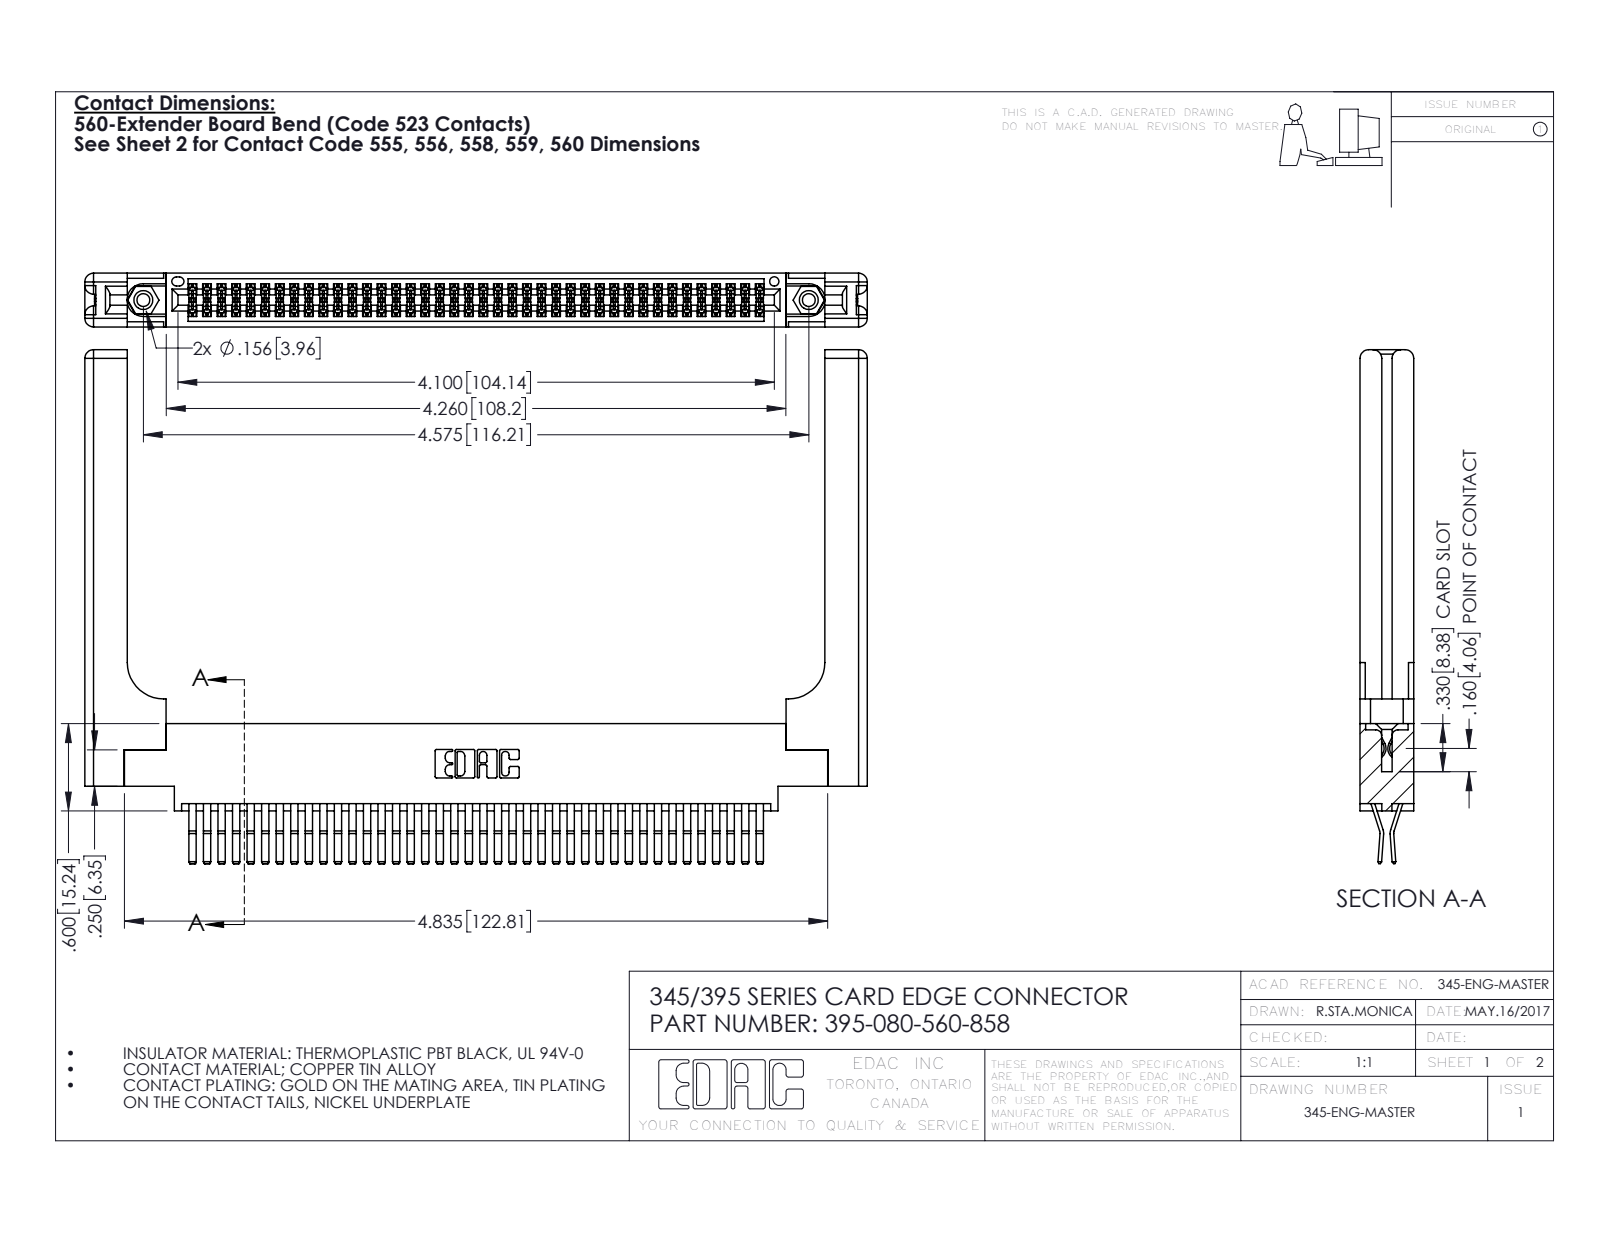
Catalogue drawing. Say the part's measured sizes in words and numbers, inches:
The part is named "345 Part_0.170 Offset - 0.156 Dia-TH; 345-250-001_345-250-001-102; 395-080-560-858; 345-292-001_560 Tail (+1 more)". Its 3-D file was written by "SolidWorks 2016 (CONFIG_CONTROL_DESIGN)". It is 85 solids with 4546 faces: 2872 planar, 1614 cylindrical and 60 other. Overall it measures 5.379 by 3.532 by 0.37 inches. Its volume is 1.351 cubic inches and its surface area 41.4 square inches. Round holes: 2 of diameter 0.089, 2 of diameter 0.125, 2 of diameter 0.156, 1 of diameter 0.064. Round bosses or shafts: 2 of diameter 0.155. Partial cylindrical surfaces (rounded edges, fillets, slot ends): 121 of radius 0.006, 22 of radius 0.01, 16 of radius 0.06, 6 of radius 0.007, 6 of radius 0.031, 3 of radius 0.026, 2 of radius 0.01, 2 of radius 0.014. The main face-to-face distances are 0.37, 0.072, 0.298, 0.025, 0.098, 0.272, 0.2, 0.225, 0.148, 0.15. The hole center spacings are 0.27, 4.339, 4.575.
